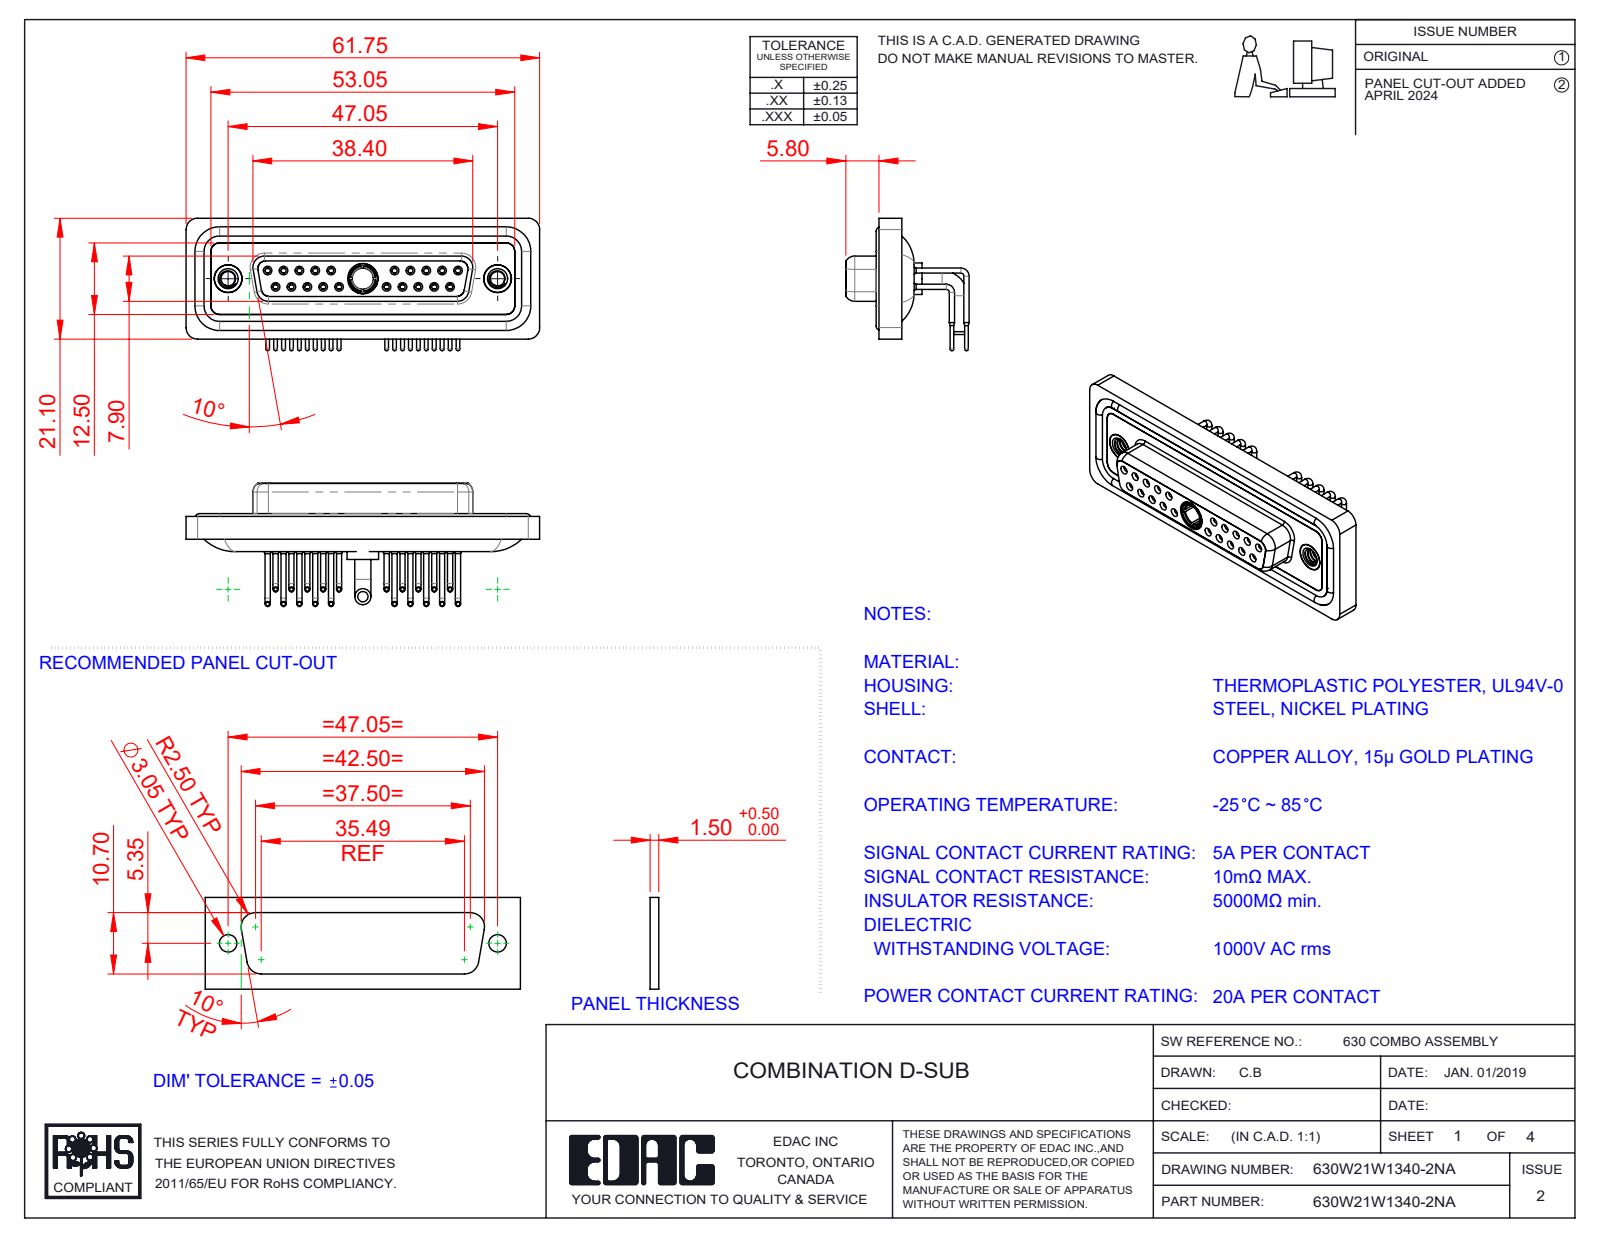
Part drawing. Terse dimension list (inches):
name: 630Combo Shell Front_25 Contacts; Power Socket_20A RA; 630Combo Waterproof Housing_25 Contacts; 630Combo Housing_21W1 (+5 more)
written by: SolidWorks 2023 (CONFIG_CONTROL_DESIGN)
unit: in
bodies: 29 solids, 1518 faces (434 planar, 671 cylindrical, 413 other)
size: 2.431 × 0.91 × 0.848
volume: 0.519 in³; area: 22.91 in²
holes: 20× ⌀0.035, 20× ⌀0.043, 20× ⌀0.059, 20× ⌀0.079, 10× ⌀0.063, 10× ⌀0.067, 3× ⌀0.191, 2× ⌀0.098, 2× ⌀0.157, 2× ⌀0.159, 2× ⌀0.197, 1× ⌀0.146
bosses: 20× ⌀0.035, 20× ⌀0.026, 14× ⌀0.063, 2× ⌀0.195, 2× ⌀0.189, 2× ⌀0.11, 1× ⌀0.217, 1× ⌀0.205
rounds: 18× R0.059, 18× R0.079, 8× R0.053, 8× R0.063, 4× R0.01, 4× R0.02, 4× R0.024, 4× R0.026
face distances: 0.016, 0.071, 0.161, 0.063, 0.043, 0.098, 0.122, 0.059, 0.386, 0.018
hole spacings: 0.124, 0.109, 0.218, 0.327, 0.198, 0.763, 0.826, 0.872
